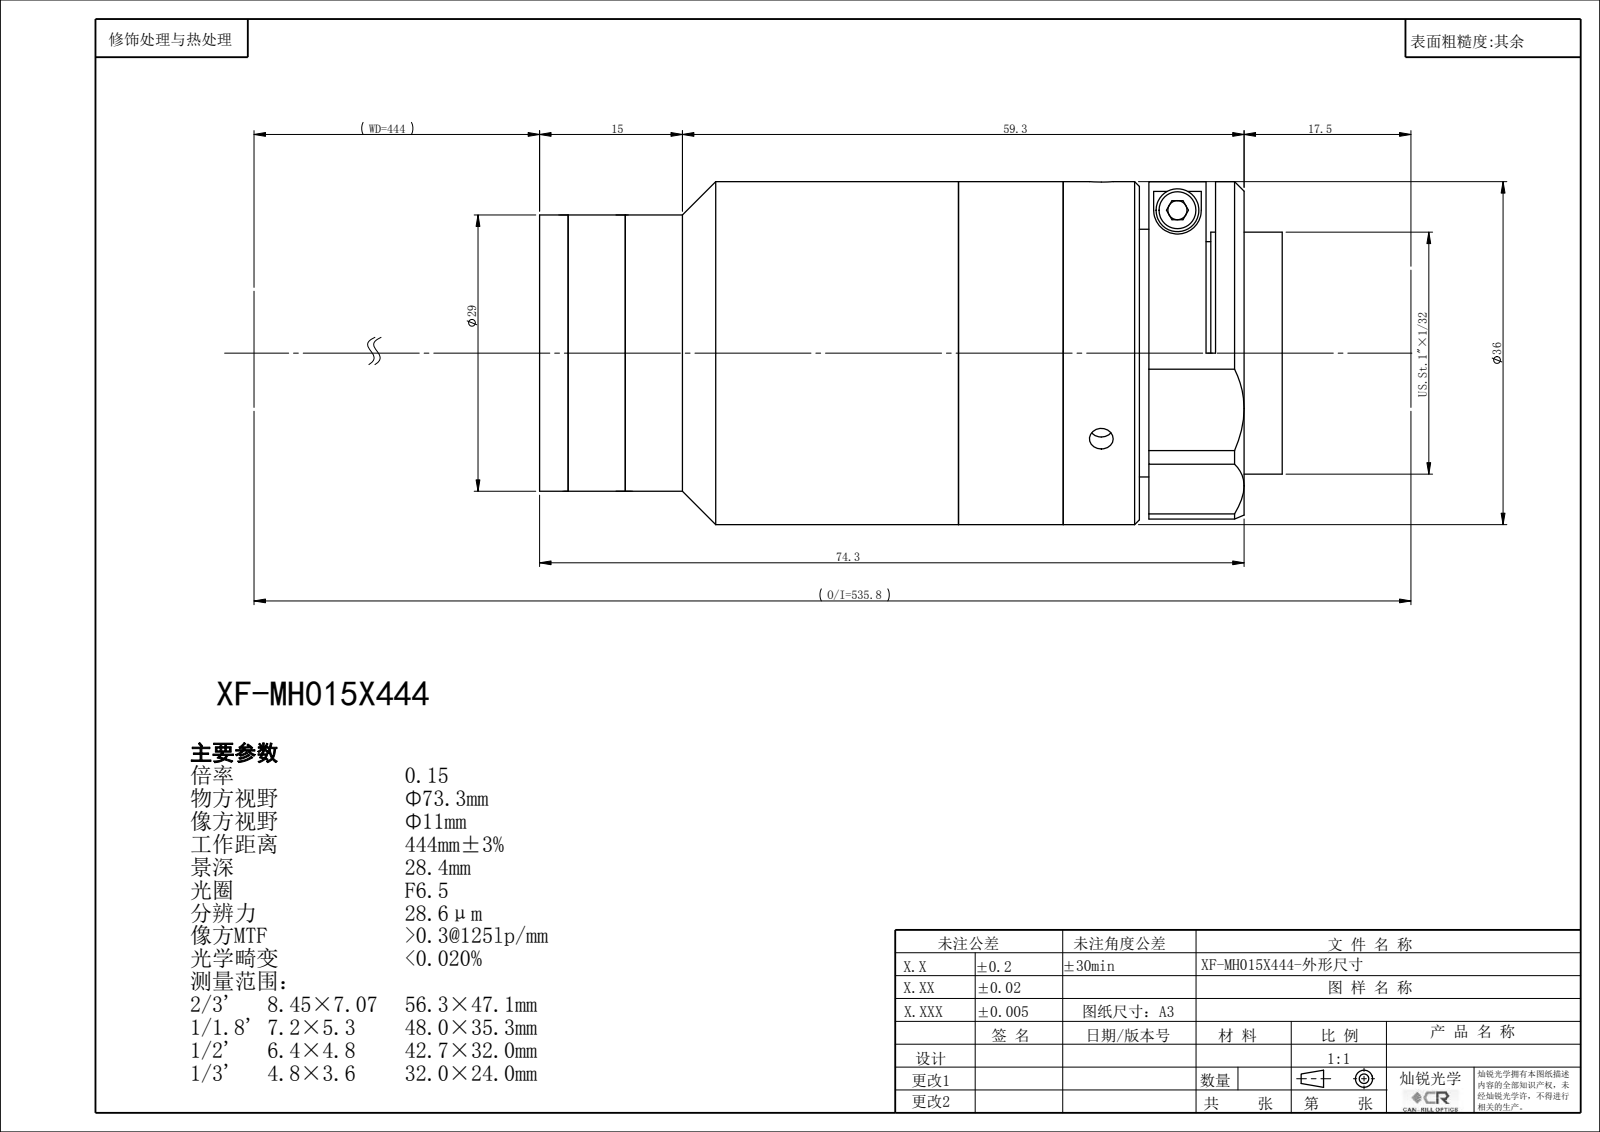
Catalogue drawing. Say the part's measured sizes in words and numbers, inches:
The part is named "XF-MH015X444". Its 3-D file was written by "SolidWorks 2022 (CONFIG_CONTROL_DESIGN)". It is 0 solids with 123 faces: 61 planar, 40 cylindrical and 22 other. Overall it measures 3.084 by 1.417 by 1.417 inches. Round holes: 3 of diameter 0.098, 1 of diameter 0.709, 1 of diameter 0.882, 1 of diameter 0.945, 1 of diameter 0.98, 1 of diameter 1.039. Round bosses or shafts: 1 of diameter 1.417, 1 of diameter 1.339, 1 of diameter 1.142, 1 of diameter 1. The main face-to-face distances are 0.761, 0.059, 0.702, 0.433, 1.135, 1.194, 2.73, 1.594, 2.028, 2.789.
